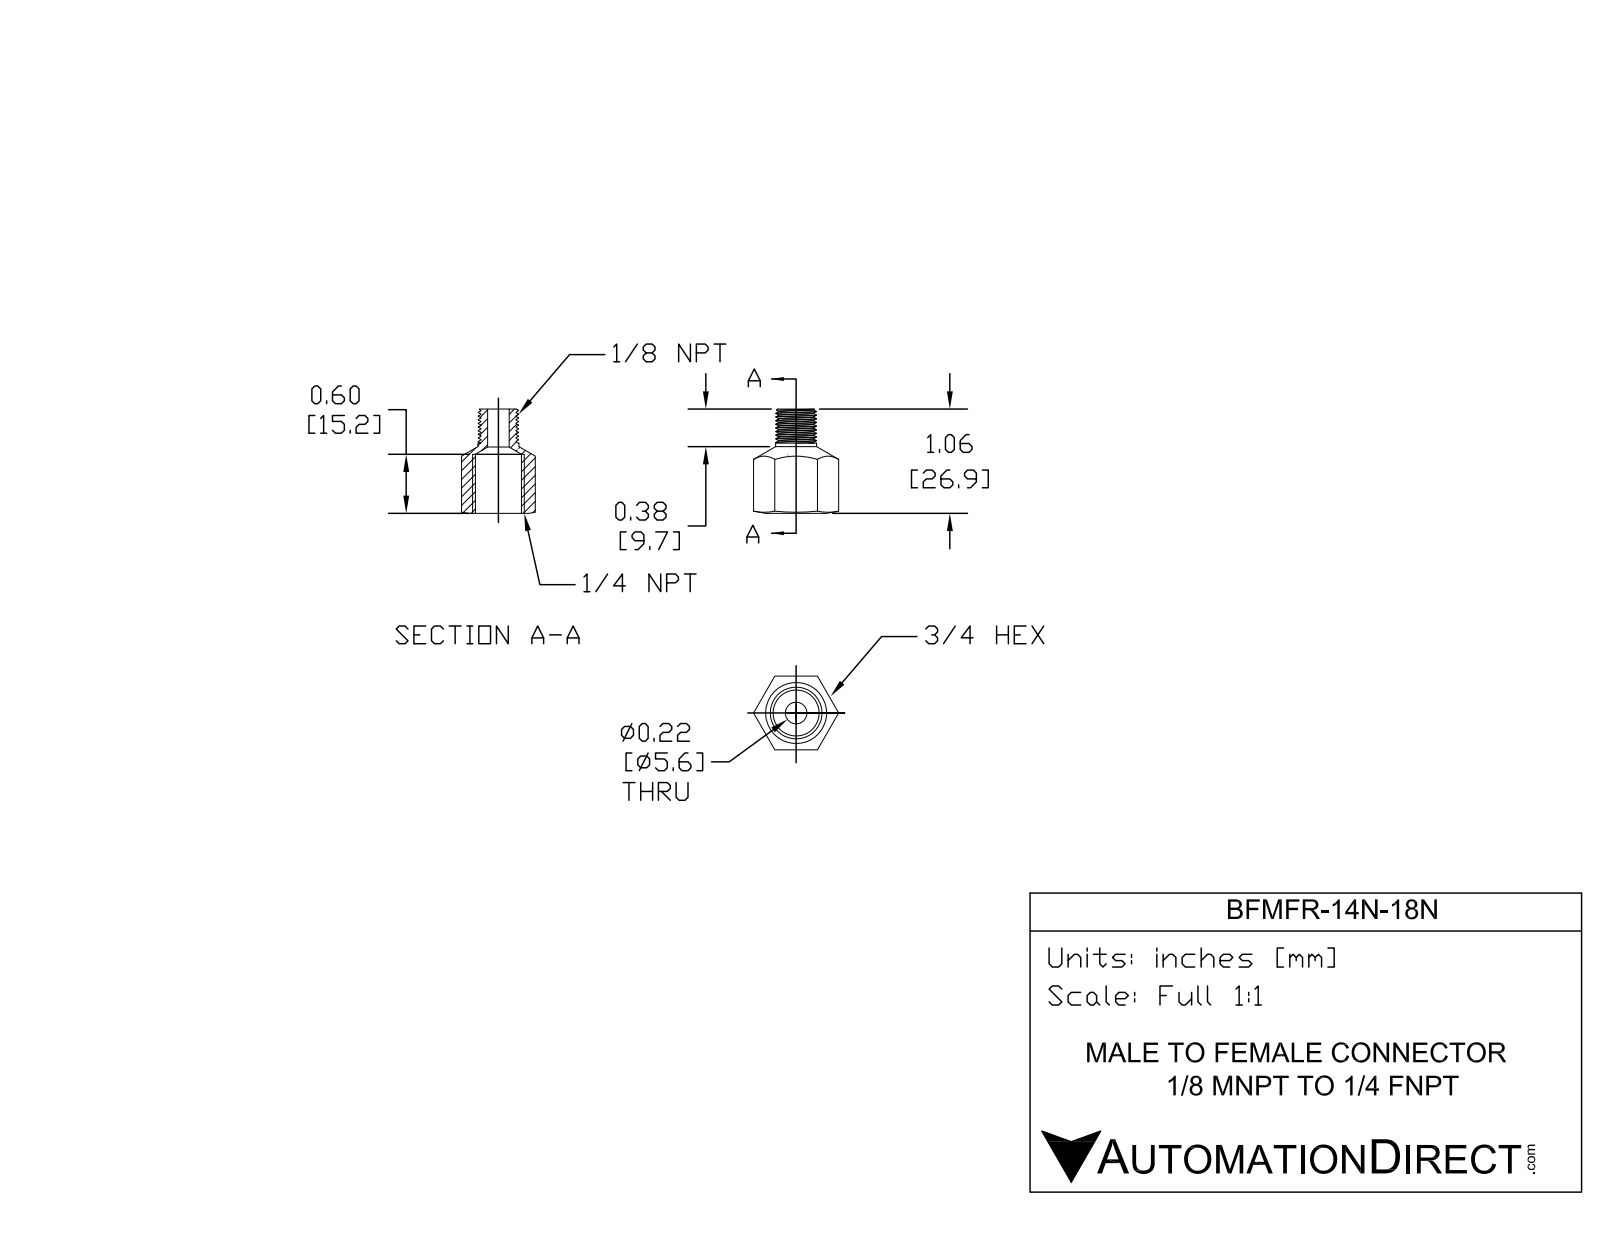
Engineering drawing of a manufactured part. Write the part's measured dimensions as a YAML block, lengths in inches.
part_name: "BFMFR-14N-18N"
step_written_by: "SolidWorks 2015 (AUTOMOTIVE_DESIGN)"
units: inches
bodies: {solids: 1, faces: 52, planar: 11, cylindrical: 25, other: 16}
overall_size: [1.06, 0.866, 0.75]
volume: 0.228
surface_area: 4.402
round_holes:
  - {diameter: 0.22, count: 1}
  - {diameter: 0.468, count: 1}
round_bosses_or_shafts:
  - {diameter: 0.416, count: 1}
  - {diameter: 0.41, count: 1}
face_to_face_distances: [0.75, 0.75, 1.06, 0.714, 0.346, 0.661, 0.053, 0.399]
